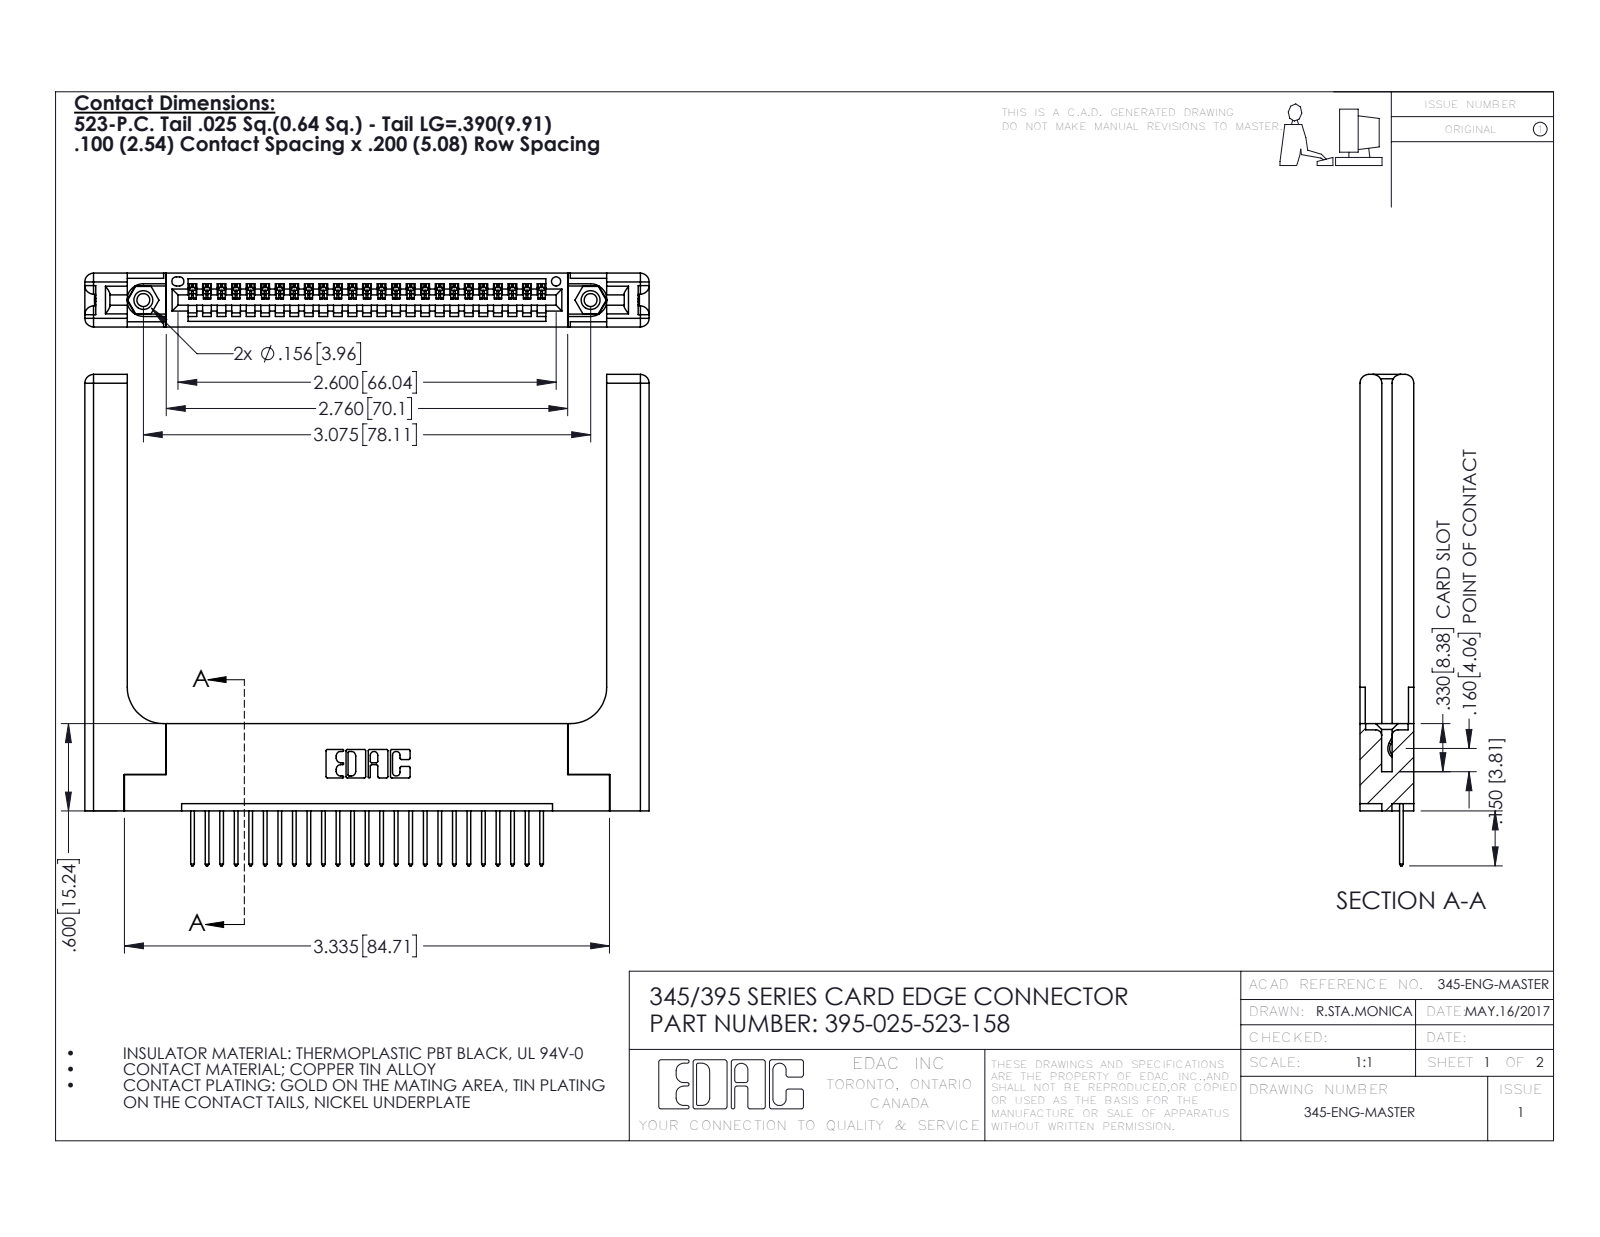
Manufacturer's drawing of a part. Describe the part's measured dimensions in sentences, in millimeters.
The part is named "345-220-058_345-220-058; 345-250-001_345-250-001-102; 345-292-001_345-293-123; 395-025-523-158 (+1 more)". Its 3-D file was written by "SolidWorks 2016 (CONFIG_CONTROL_DESIGN)". It is 30 solids with 1832 faces: 1228 planar, 544 cylindrical and 60 other. Overall it measures 98.5 by 85.8 by 9.4 millimeters. Its volume is 17 710 cubic millimeters and its surface area 17 340 square millimeters. Round holes: 2 of diameter 2.3, 2 of diameter 3.2, 2 of diameter 4, 1 of diameter 1.6. Round bosses or shafts: 2 of diameter 3.9. Partial cylindrical surfaces (rounded edges, fillets, slot ends): 50 of radius 0.2, 50 of radius 0.3, 22 of radius 0.3, 16 of radius 1.5, 6 of radius 0.2, 6 of radius 0.8, 3 of radius 0.7, 2 of radius 0.8. The main face-to-face distances are 9.4, 1.8, 7.6, 5.1, 3.8, 3.8, 2.5, 6.9, 0.6, 2. The hole center spacings are 6.9, 72.1, 78.1.
